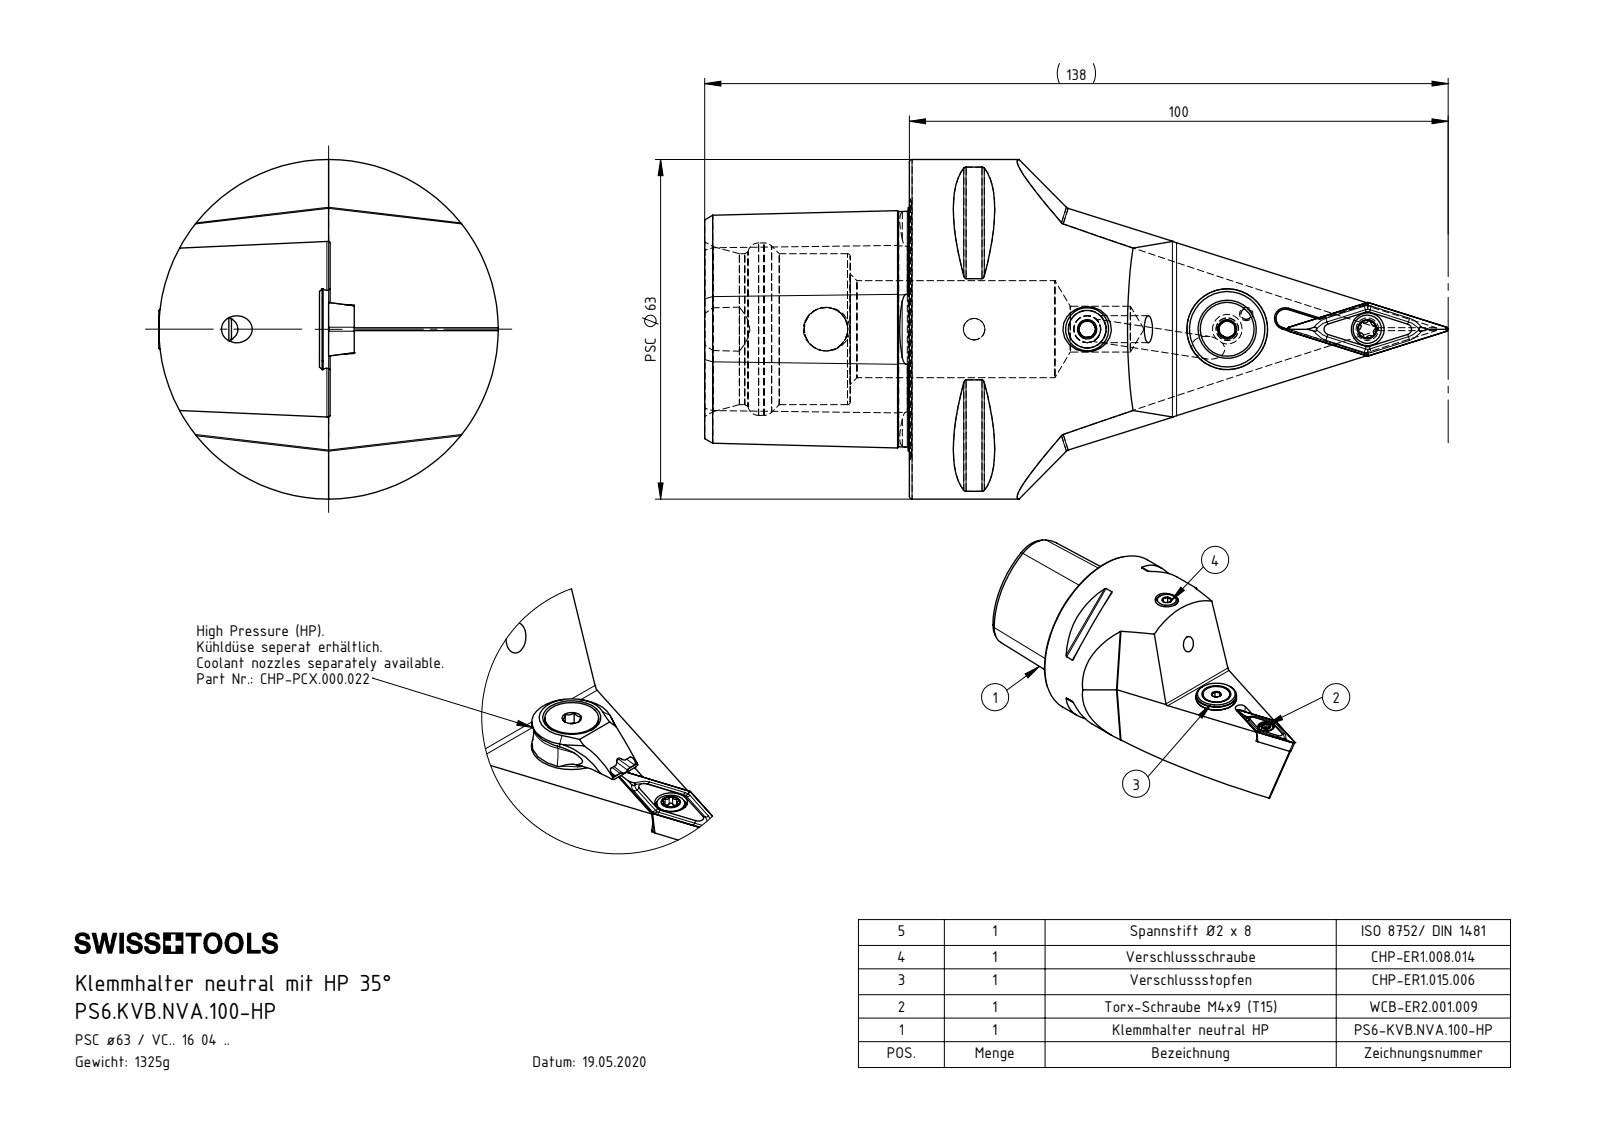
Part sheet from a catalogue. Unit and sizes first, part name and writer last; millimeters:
Units: millimetres
Overall size (bounding box): 138 × 63 × 63
Round holes (diameter × count): ⌀4.2 ×2, ⌀5 ×2, ⌀1.2 ×1, ⌀2 ×1, ⌀2.5 ×1, ⌀3 ×1, ⌀3.3 ×1, ⌀4 ×1, ⌀4.4 ×1, ⌀5.2 ×1, ⌀6.1 ×1, ⌀7 ×1
Round bosses / shafts (diameter × count): ⌀63 ×1, ⌀15 ×1, ⌀13.4 ×1, ⌀10 ×1, ⌀8 ×1, ⌀5.5 ×1, ⌀5.25 ×1, ⌀5 ×1
Partial cylindrical surfaces — rounded edges, fillets, slot ends (radius × count): R0.5 ×10, R0.34 ×6, R0.59 ×6, R0.8 ×2, R1.75 ×1, R6 ×1, R7 ×1
Main face-to-face distances: 38, 24.88, 4.5, 27, 11, 4.46, 55.8, 37.8, 10.8, 6.4
Hole centre spacings: 4.5, 20.09, 21.59, 21.69, 23.76, 24.9, 25, 27.5
Volume: 185 011 mm³ · Surface area: 32 581 mm²
Bodies: 8 solids, 277 faces (93 planar, 63 cylindrical, 121 other)
Part name (STEP PRODUCT): PS6.KVB.NVA.100-HP; ISO 8752 2x8; DIN 3771 - 13x1; DIN 7991 - M5x15 (+6 more)
STEP written by: SolidWorks 2017 (AUTOMOTIVE_DESIGN)
